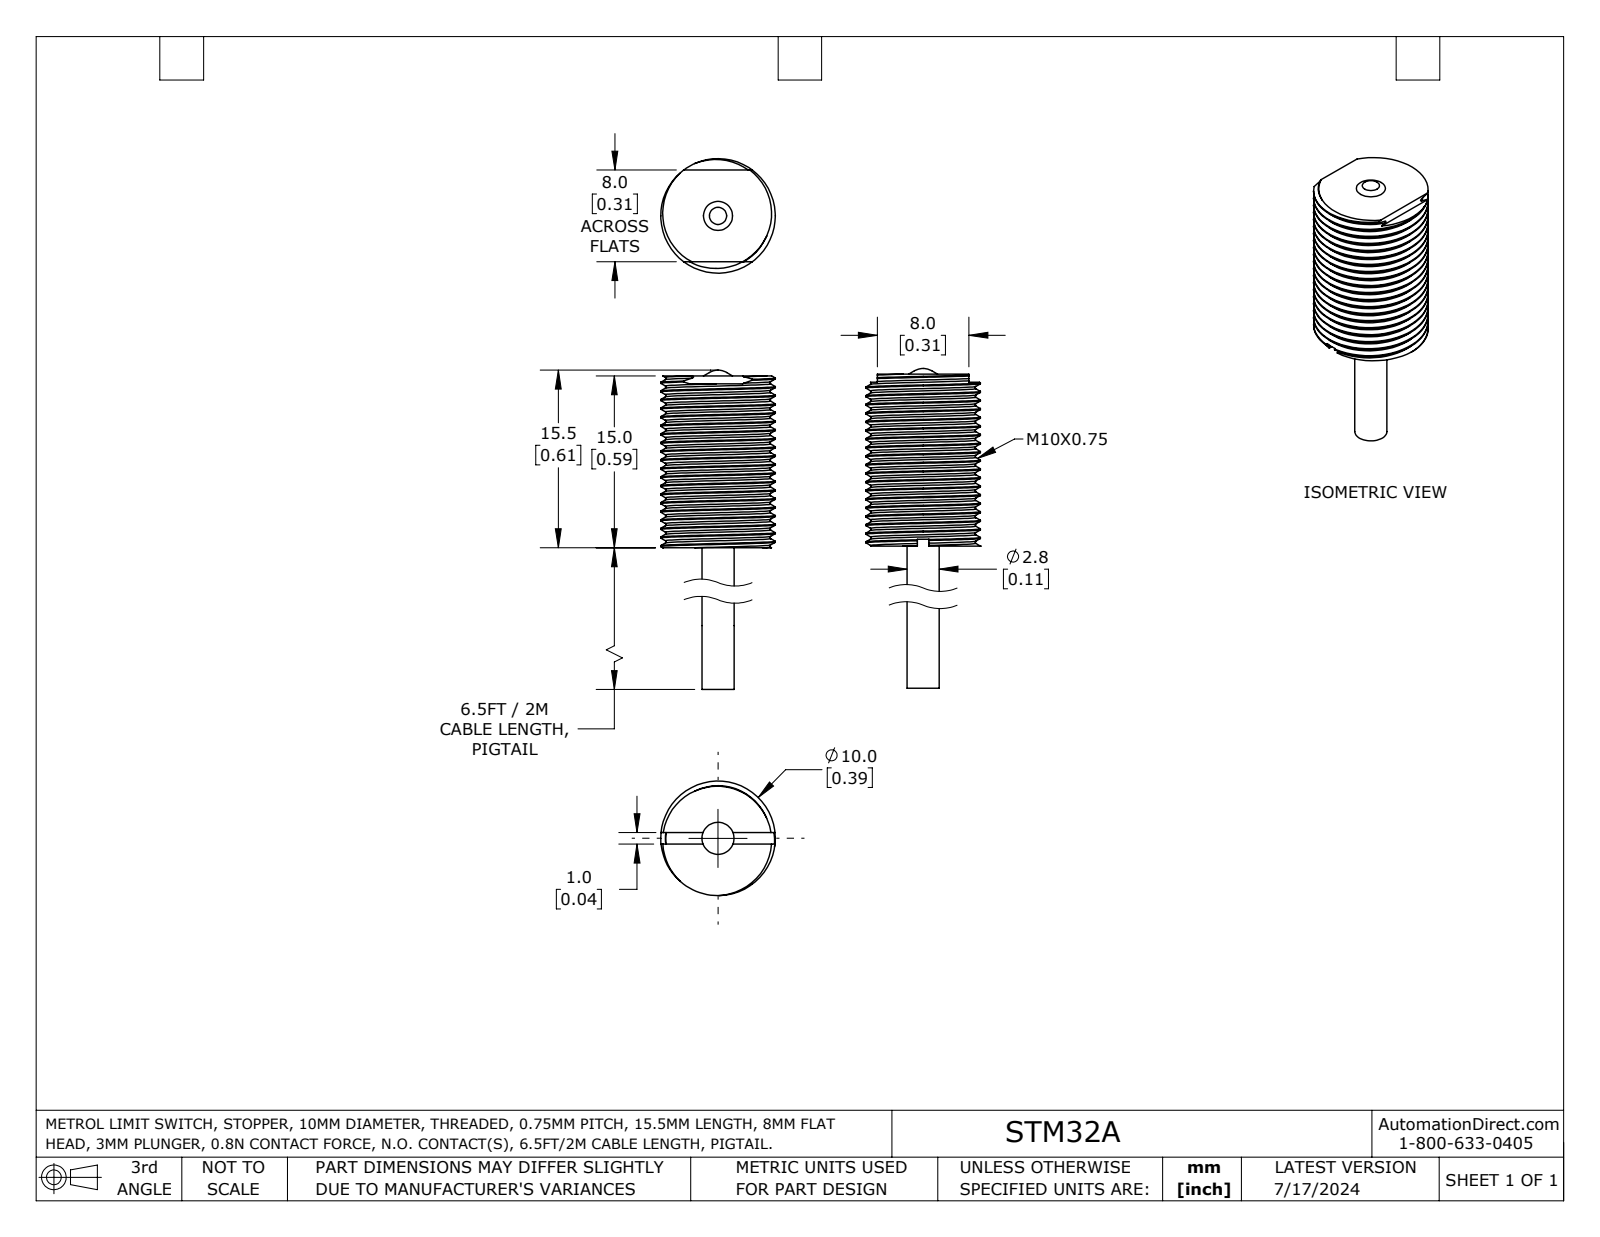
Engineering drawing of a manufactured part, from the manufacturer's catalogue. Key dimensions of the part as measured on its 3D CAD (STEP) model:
Part name (STEP PRODUCT): STM32A
STEP written by: SolidWorks 2023 (AUTOMOTIVE_DESIGN)
Units: inches
Bodies: 1 solid, 76 faces (14 planar, 44 cylindrical, 18 other)
Overall size (bounding box): 0.823 × 0.394 × 0.394
Volume: 0.067 in³ · Surface area: 1.467 in²
Round bosses / shafts (diameter × count): ⌀0.394 ×1, ⌀0.11 ×1
Main face-to-face distances: 0.591, 0.138, 0.177, 0.567, 0.024, 0.803, 0.236, 0.213, 0.028, 0.539
